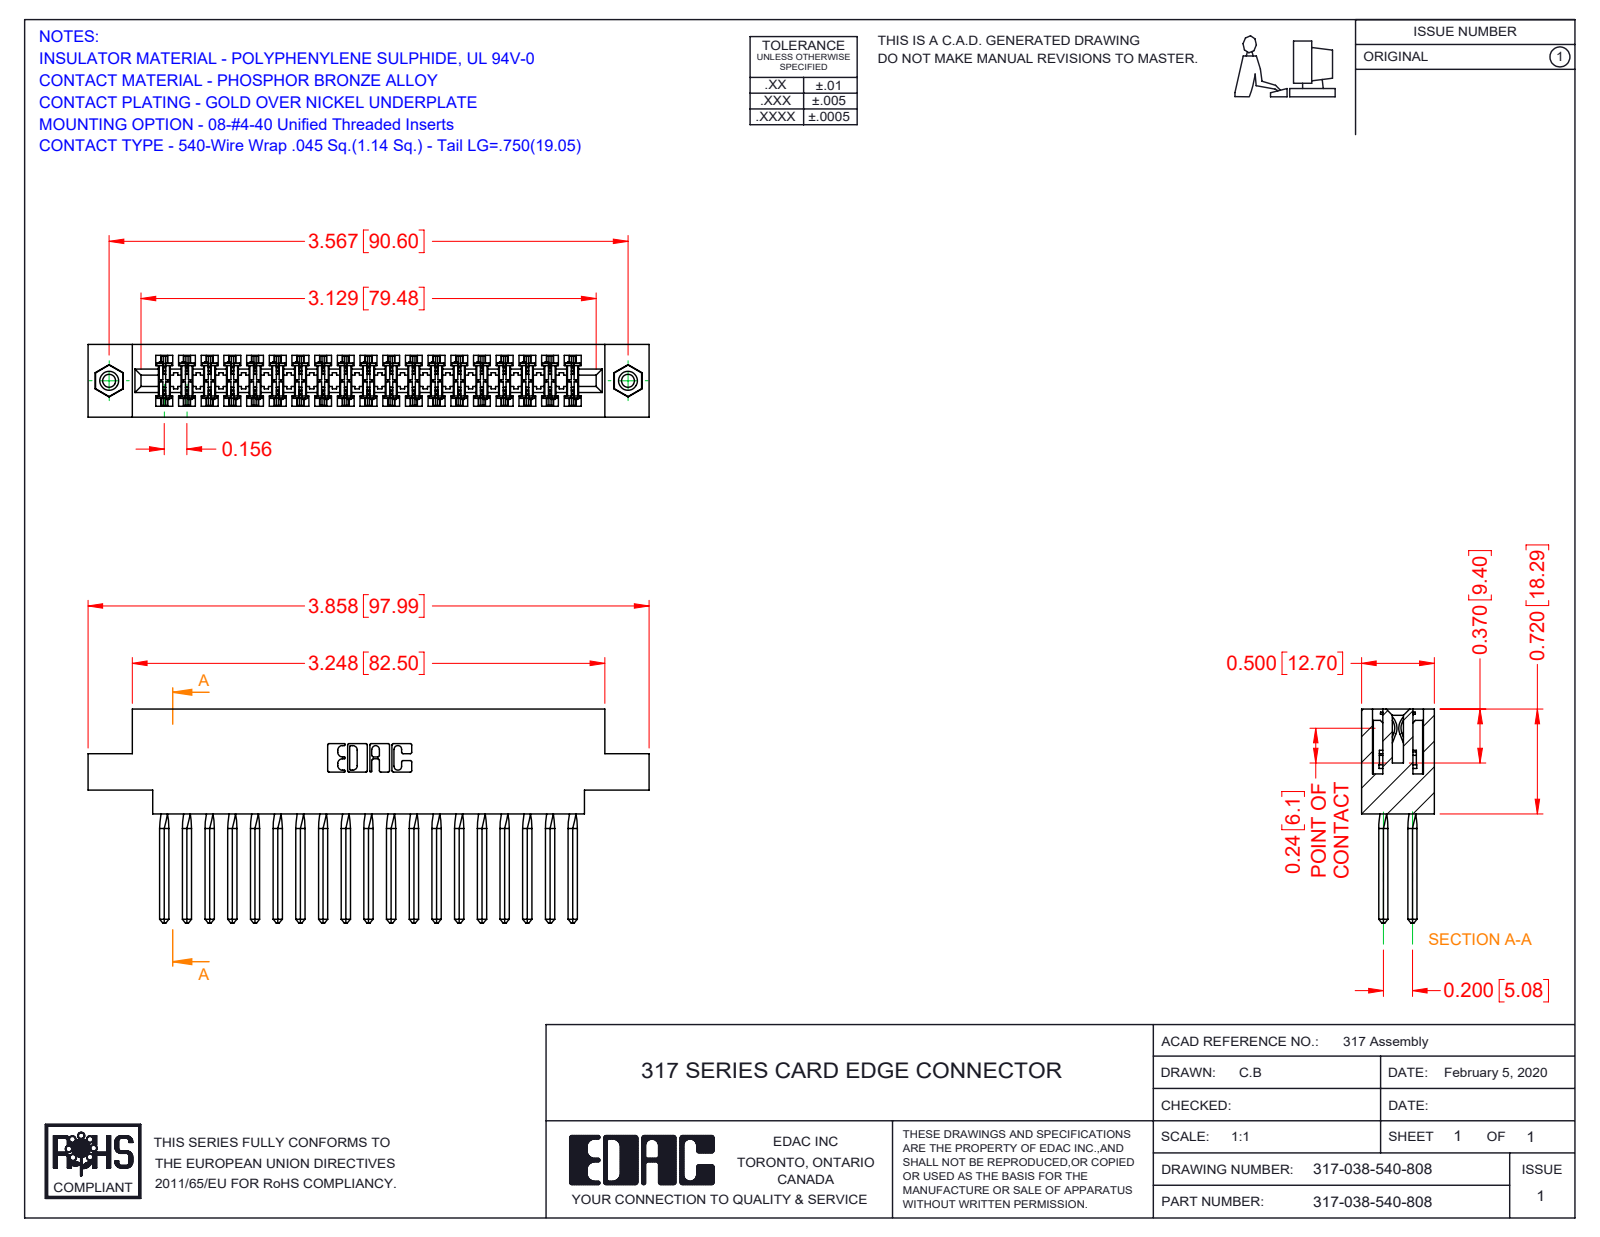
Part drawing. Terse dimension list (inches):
name: 317-038-540-808; 317 Part_.156 Dia - TI; 345-250-001_345-250-003-102; 317-290-001_540
written by: SolidWorks 2016 (CONFIG_CONTROL_DESIGN)
unit: in
bodies: 41 solids, 3544 faces (2864 planar, 512 cylindrical, 168 other)
size: 3.858 × 1.47 × 0.5
volume: 0.956 in³; area: 34.88 in²
holes: 2× ⌀0.089, 2× ⌀0.125, 2× ⌀0.156
bosses: 2× ⌀0.155
rounds: 76× R0.015, 22× R0.01, 6× R0.007, 6× R0.031, 3× R0.026, 2× R0.095, 2× R0.1, 2× R0.11
face distances: 0.5, 0.075, 0.425, 0.11, 0.35, 0.195, 0.22, 0.72, 0.136, 0.094
hole spacings: 3.567
